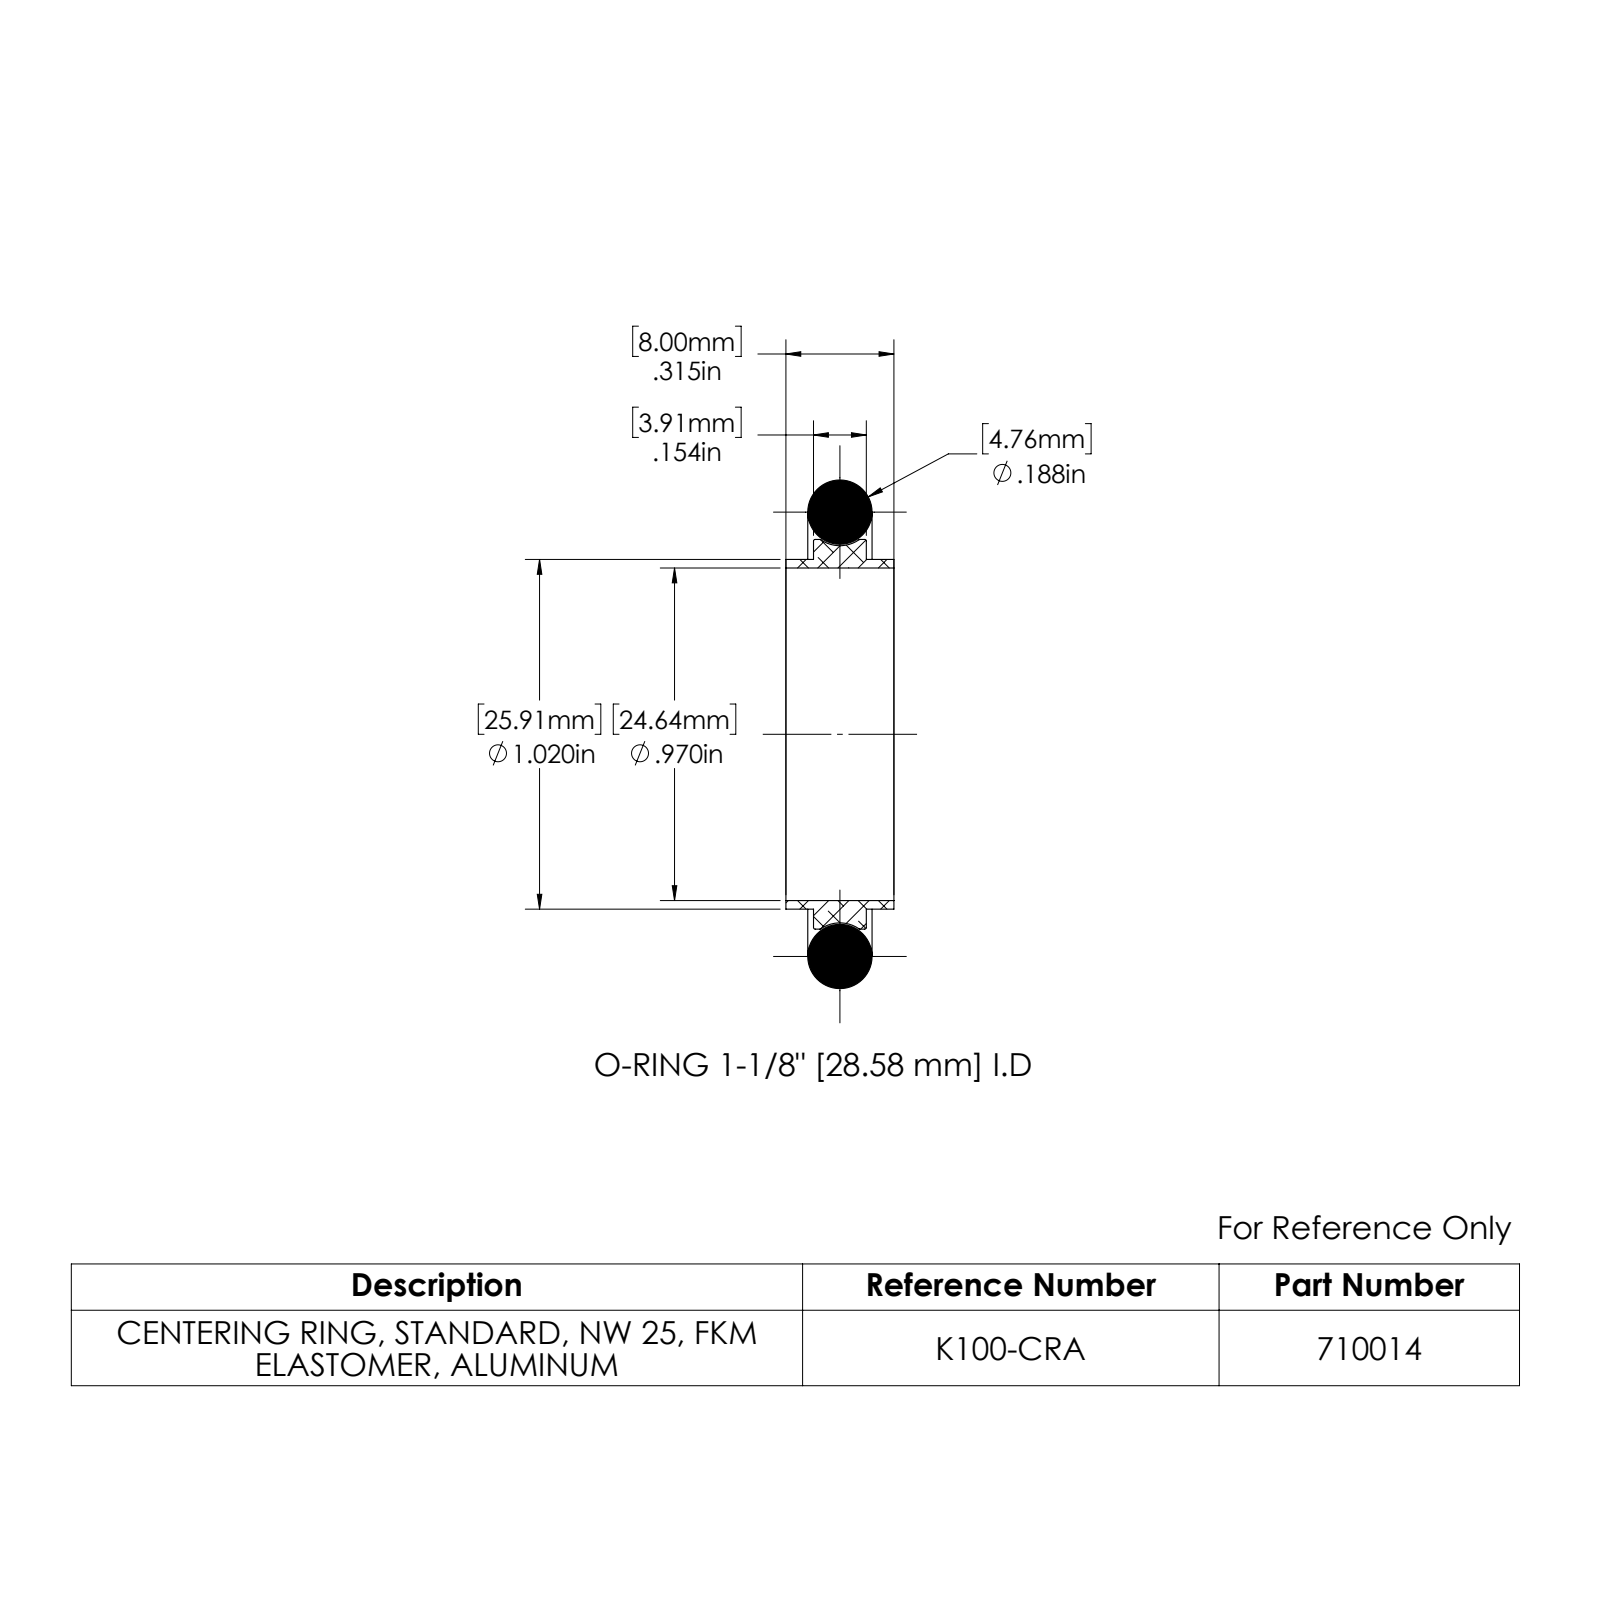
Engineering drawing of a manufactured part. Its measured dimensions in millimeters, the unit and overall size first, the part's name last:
Units: millimetres
Overall size (bounding box): 37.7 × 37.7 × 8
Round holes (diameter × count): ⌀24.6 ×1
Round bosses / shafts (diameter × count): ⌀28.9 ×1, ⌀25.9 ×1
Main face-to-face distances: 3.9, 2, 6, 8
Volume: 2 650 mm³ · Surface area: 3 211 mm²
Bodies: 2 solids, 30 faces (4 planar, 10 cylindrical, 16 other)
Part name (STEP PRODUCT): 710014
STEP written by: SolidWorks 2022 (AUTOMOTIVE_DESIGN)
